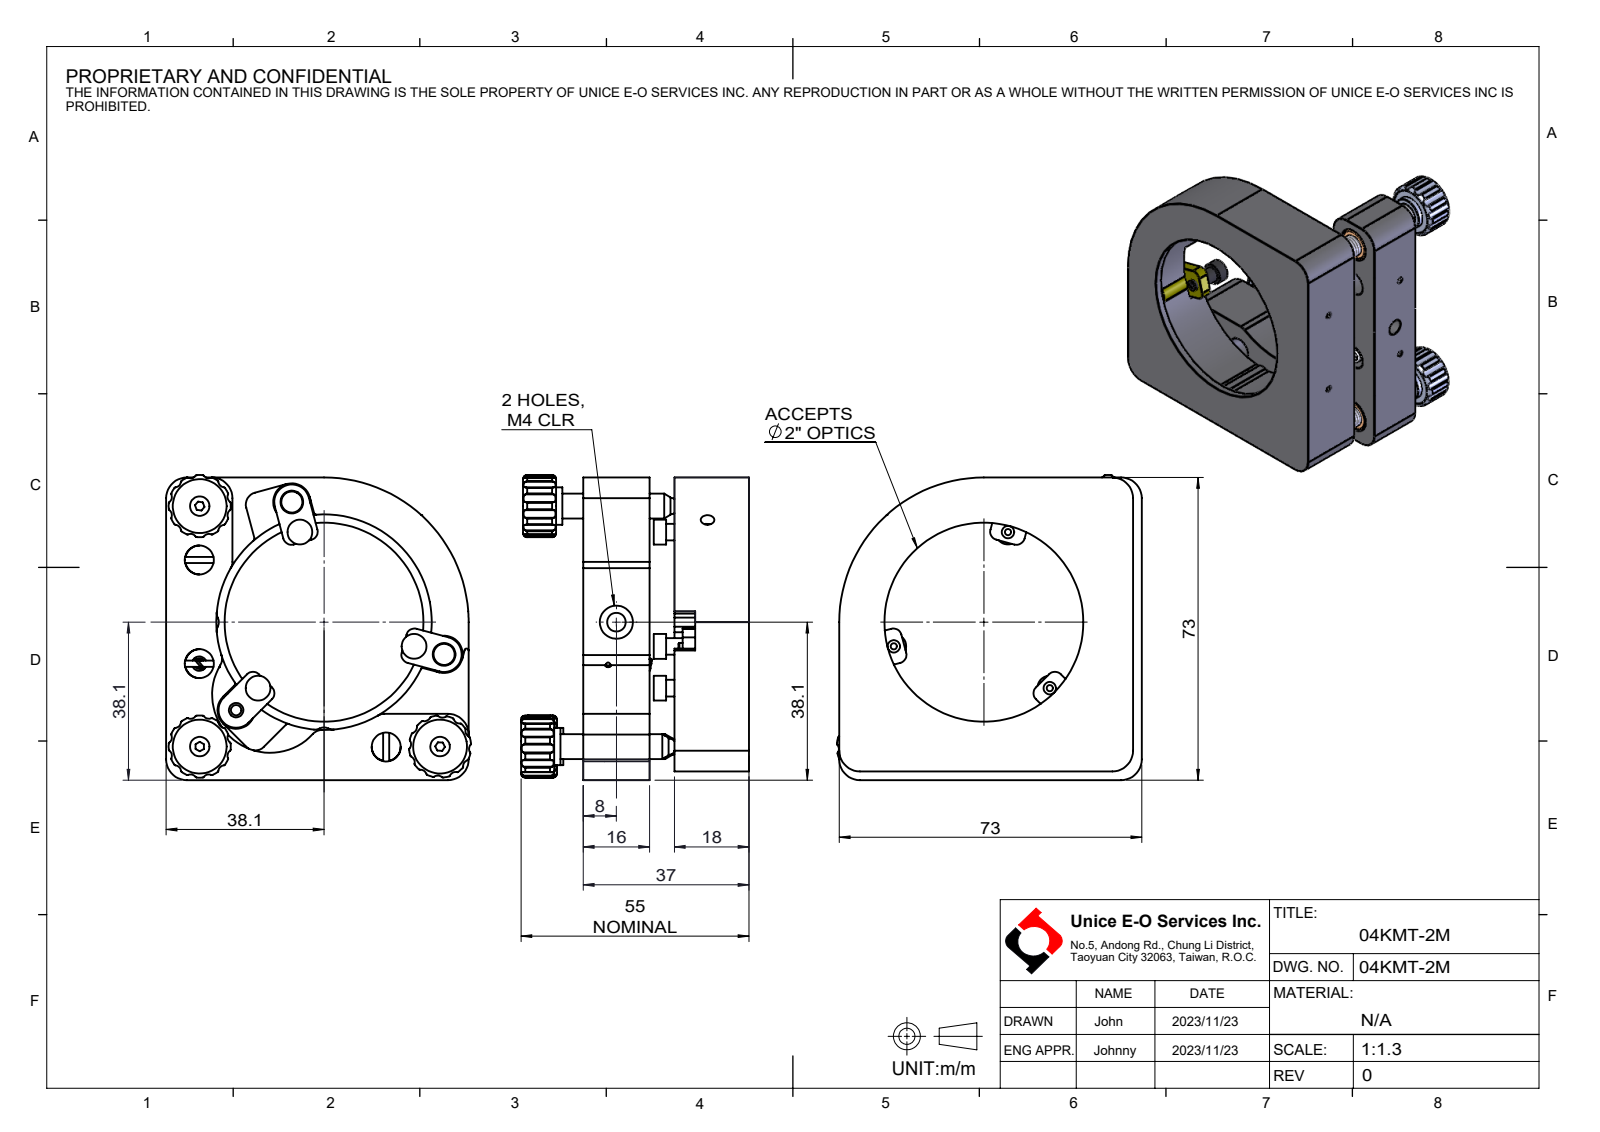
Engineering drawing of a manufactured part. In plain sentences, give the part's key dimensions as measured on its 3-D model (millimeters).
The part is named "04KMT-2M". Its 3-D file was written by "SolidWorks 2016 (CONFIG_CONTROL_DESIGN)". It is 36 solids with 808 faces: 209 planar, 448 cylindrical and 151 other. Overall it measures 73.6 by 73.6 by 54.96 millimeters. Its volume is 74 830 cubic millimeters and its surface area 38 084 square millimeters. Round holes: 9 of diameter 7, 6 of diameter 1, 6 of diameter 1.7, 6 of diameter 2.5, 6 of diameter 6, 3 of diameter 1.5, 3 of diameter 3.5, 3 of diameter 4, 3 of diameter 4.7, 3 of diameter 5.9, 3 of diameter 9, 3 of diameter 9.5. Round bosses or shafts: 8 of diameter 1.5, 6 of diameter 3, 4 of diameter 4, 3 of diameter 9, 3 of diameter 8.5, 3 of diameter 6, 3 of diameter 5.5, 2 of diameter 0.6. Partial cylindrical surfaces (rounded edges, fillets, slot ends): 72 of radius 0.3, 37 of radius 1.5, 8 of radius 0.5, 8 of radius 5, 7 of radius 3, 6 of radius 2, 6 of radius 2.5, 4 of radius 0.75. The main face-to-face distances are 16, 18, 2.1, 28.96, 26.96, 44.96, 10.96, 73, 70.9, 2. The hole center spacings are 25, 13, 45, 45.61, 22.5, 30, 30.96, 51.96.
